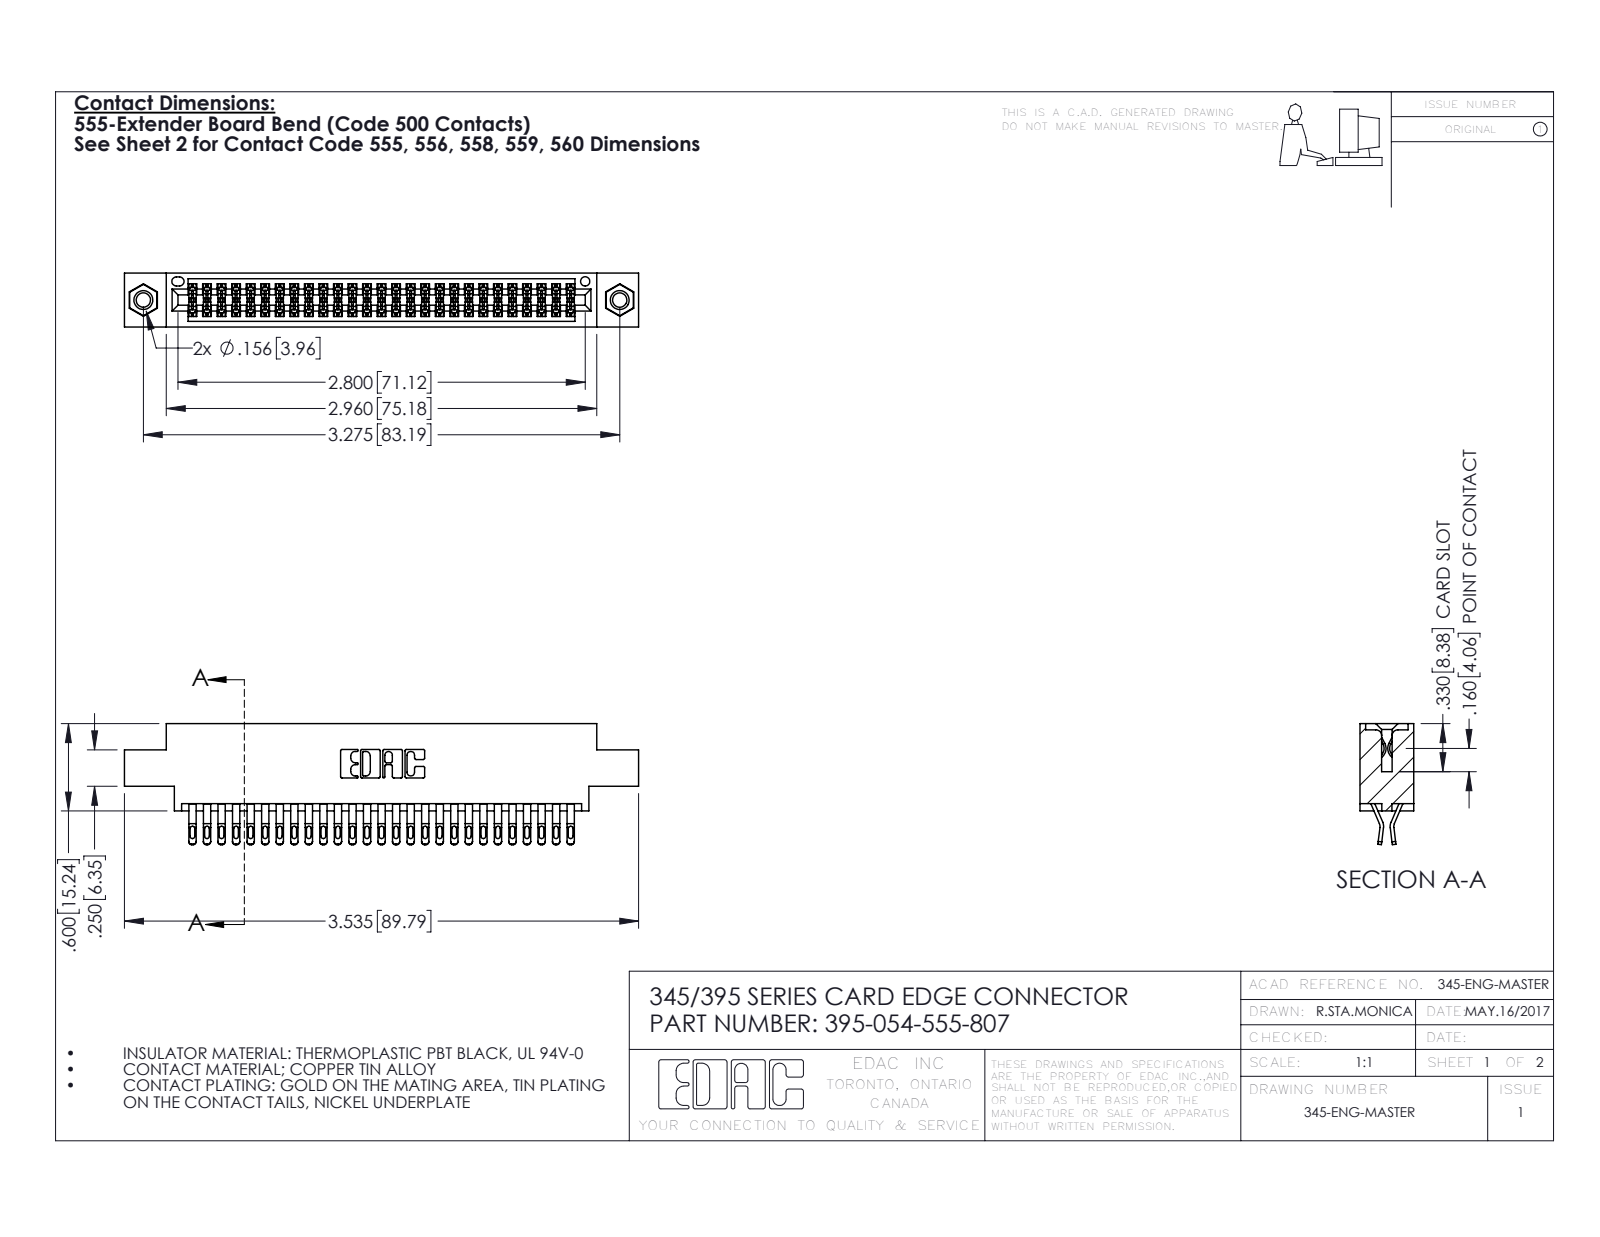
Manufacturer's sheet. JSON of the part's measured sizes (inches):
{"part_name": "345-250-001_345-250-005-103; 345-292-001_555 Tail; 395-054-555-807; 345 Part_0.170 Offset - 0.156 Dia-TI", "step_written_by": "SolidWorks 2016 (CONFIG_CONTROL_DESIGN)", "units": "inches", "bodies": {"solids": 57, "faces": 3214, "planar": 1790, "cylindrical": 1408, "other": 16}, "overall_size": [3.535, 0.832, 0.37], "volume_in3": 0.526, "surface_area_in2": 20.39, "round_holes": [[0.098, 2], [0.125, 2], [0.156, 2], [0.064, 1]], "round_bosses_or_shafts": [[0.155, 2]], "partial_cylinders_radius": [[0.016, 135], [0.02, 108], [0.006, 81], [0.01, 22], [0.007, 6], [0.031, 6], [0.026, 3], [0.01, 2]], "face_to_face_distances": [0.072, 0.298, 0.37, 0.025, 0.2, 0.098, 0.272, 0.225, 0.175, 0.149], "hole_center_spacings": [0.27, 3.04, 3.275]}
